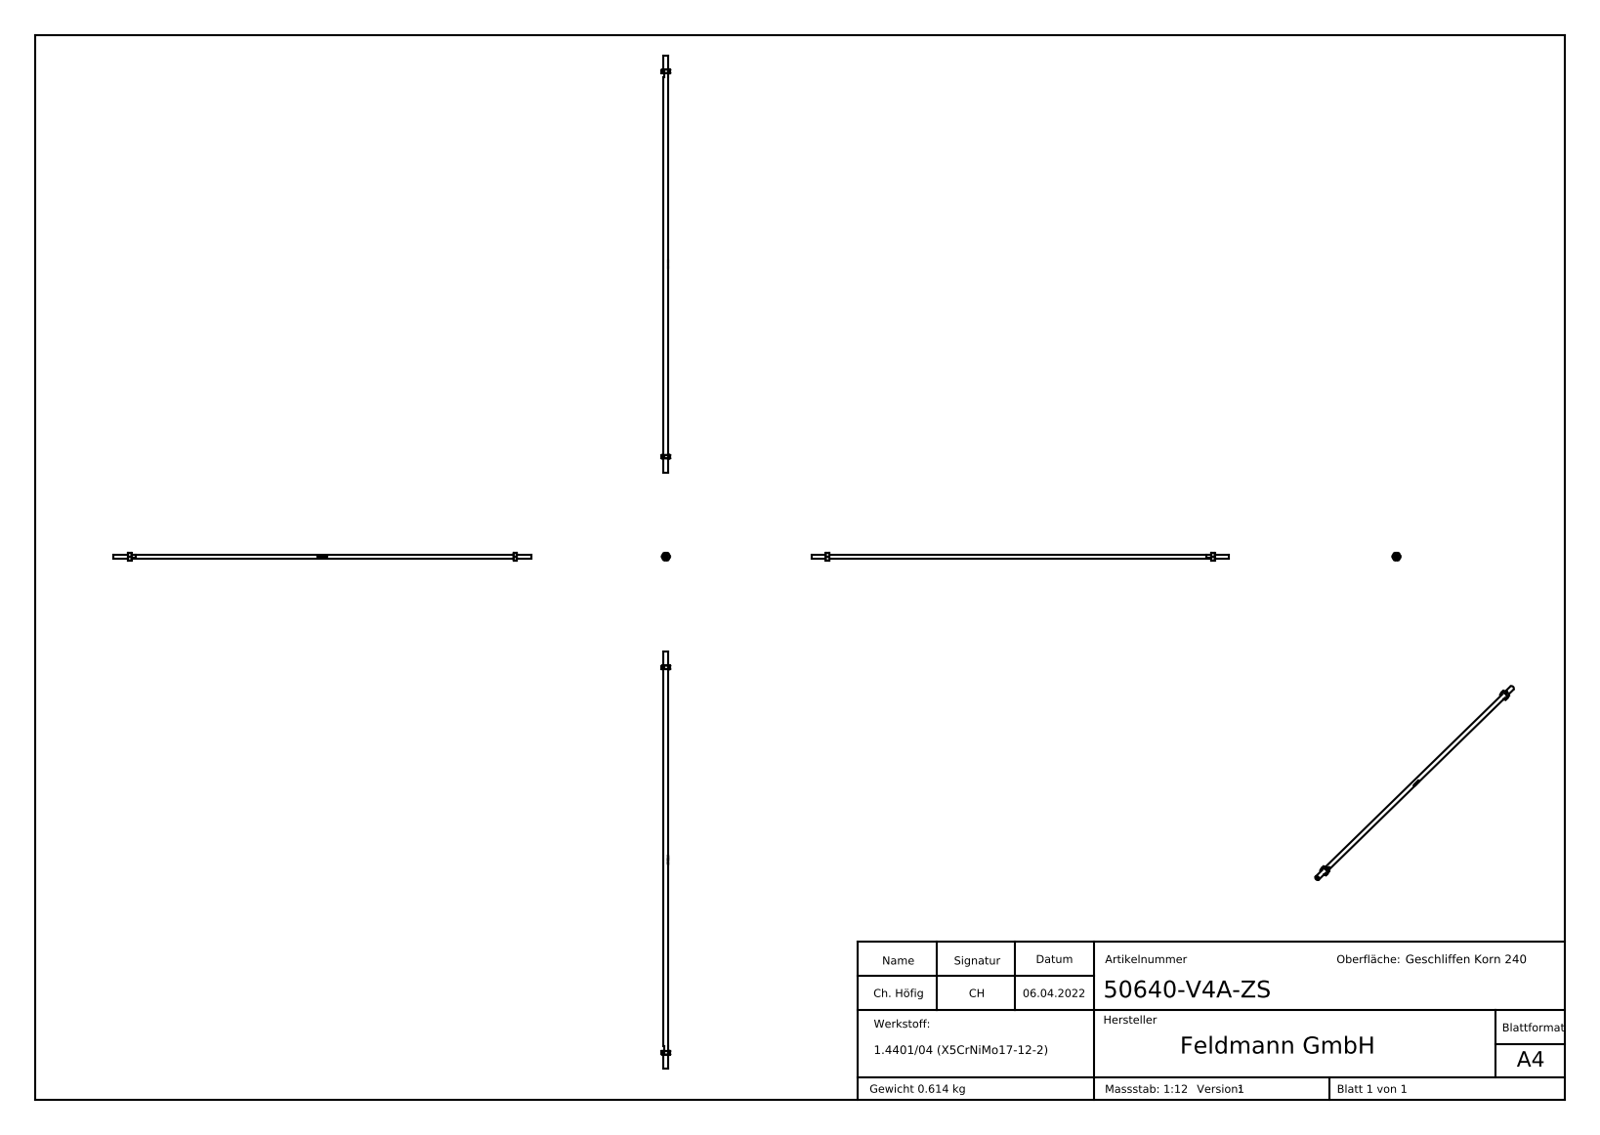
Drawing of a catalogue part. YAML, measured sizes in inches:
part_name: "50640-V4A-ZS; DIN 934 M4-M20_58321-240-10; 50640-XXX-ZS_50640-V4A-ZS"
step_written_by: "SolidWorks 2018 (CONFIG_CONTROL_DESIGN)"
units: inches
bodies: {solids: 3, faces: 1199, planar: 630, cylindrical: 31, other: 538}
overall_size: [37.008, 0.767, 0.669]
volume: 4.687
surface_area: 49.32
round_holes:
  - {diameter: 0.335, count: 1}
round_bosses_or_shafts:
  - {diameter: 0.394, count: 1}
partial_cylinders:
  - {radius: 0.02, count: 6}
face_to_face_distances: [0.669, 0.315, 34.173, 33.858, 34.488, 1.26, 1.575, 35.433, 35.748, 37.008]
